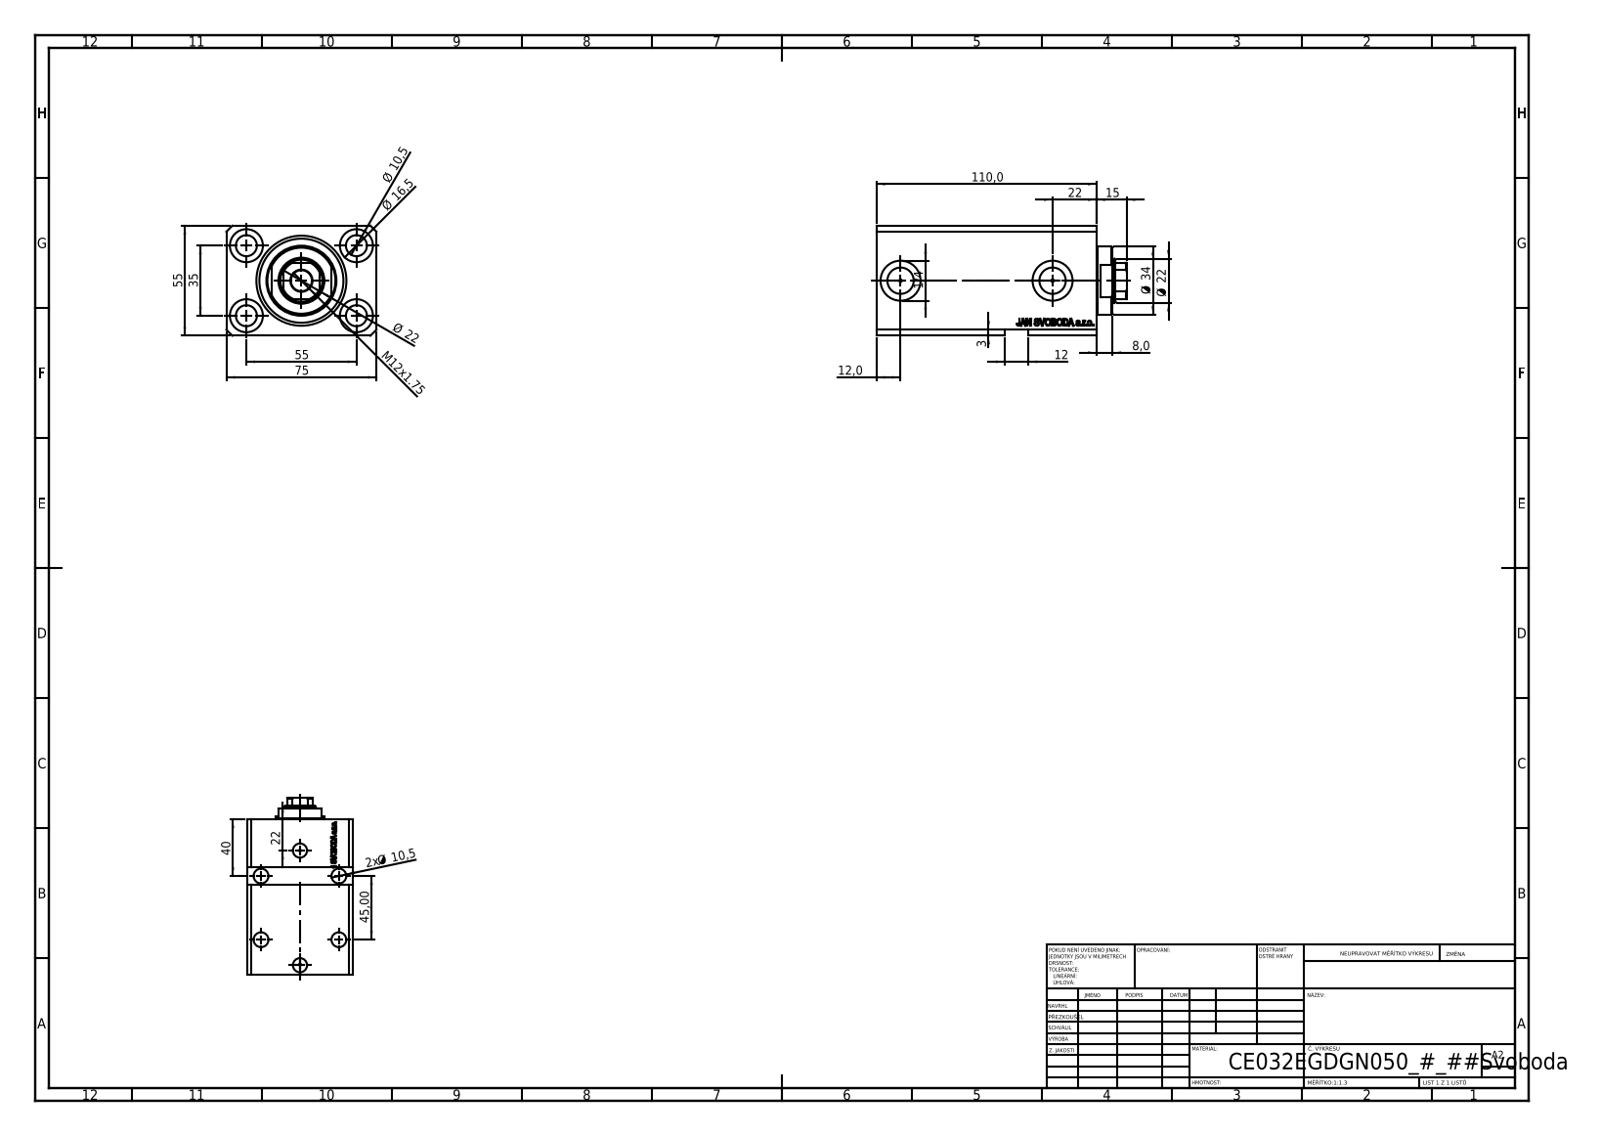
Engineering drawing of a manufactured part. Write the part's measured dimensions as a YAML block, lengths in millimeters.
part_name: "V250CE_E_Body; V250CE_VC_E; V250CE_C_VCP"
step_written_by: "SolidWorks 2019 (CONFIG_CONTROL_DESIGN)"
units: millimeters
bodies: {solids: 3, faces: 930, planar: 442, cylindrical: 116, other: 372}
overall_size: [125, 75, 55]
volume: 365493
surface_area: 86538
round_holes:
  - {diameter: 10.5, count: 9}
  - {diameter: 1.25, count: 4}
  - {diameter: 16.5, count: 4}
  - {diameter: 10, count: 2}
  - {diameter: 13.16, count: 2}
  - {diameter: 20, count: 2}
  - {diameter: 22, count: 1}
  - {diameter: 32, count: 1}
  - {diameter: 45, count: 1}
round_bosses_or_shafts:
  - {diameter: 34, count: 1}
partial_cylinders:
  - {radius: 10.5, count: 1}
face_to_face_distances: [55, 75, 15, 110, 95, 9.9, 85.1, 100.1, 11, 99]
hole_center_spacings: [32.6, 32.87, 55, 68.74, 32.58, 35, 45, 65.19]
